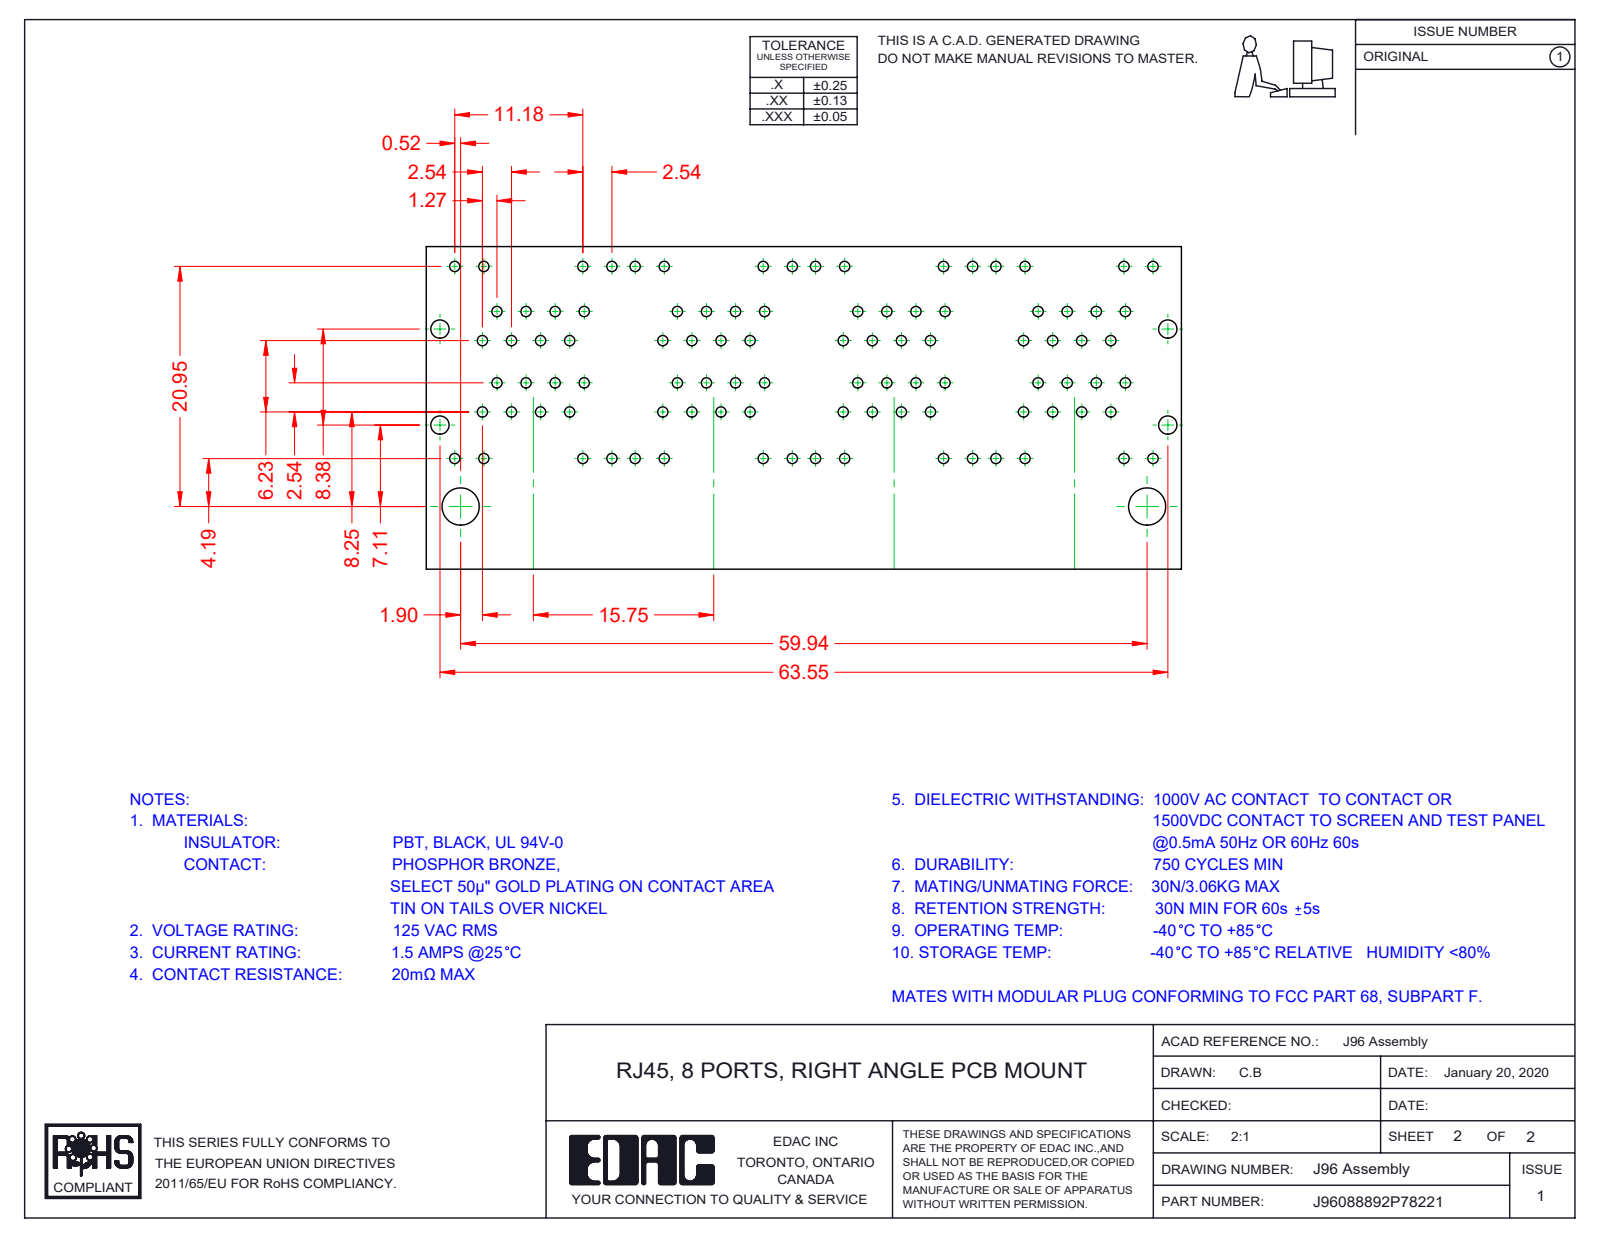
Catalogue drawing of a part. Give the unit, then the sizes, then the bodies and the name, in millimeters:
Units: millimetres
Overall size (bounding box): 67.35 × 31.38 × 28.68
Round holes (diameter × count): ⌀1.7 ×3
Round bosses / shafts (diameter × count): ⌀1.68 ×3
Partial cylindrical surfaces — rounded edges, fillets, slot ends (radius × count): R0.25 ×124, R0.35 ×73, R1 ×72, R0.5 ×49, R0.91 ×32, R0.2 ×27, R0.27 ×14, R0.7 ×11
Main face-to-face distances: 15.75, 0.35, 9.95, 1.17, 1.6, 0.54, 9.98, 10.18, 12.67, 3.37
Hole centre spacings: 15.75, 31.5
Volume: 24 149 mm³ · Surface area: 63 596 mm²
Bodies: 96 solids, 7836 faces (6105 planar, 1420 cylindrical, 311 other)
Part name (STEP PRODUCT): 96 Insulator_8 Ports; 96 Grounding_8 Ports; 96 LED LH Upper_7-Green-Orange; 96 LED LH Lower_7-Green-Orange (+8 more)
STEP written by: SolidWorks 2016 (CONFIG_CONTROL_DESIGN)
